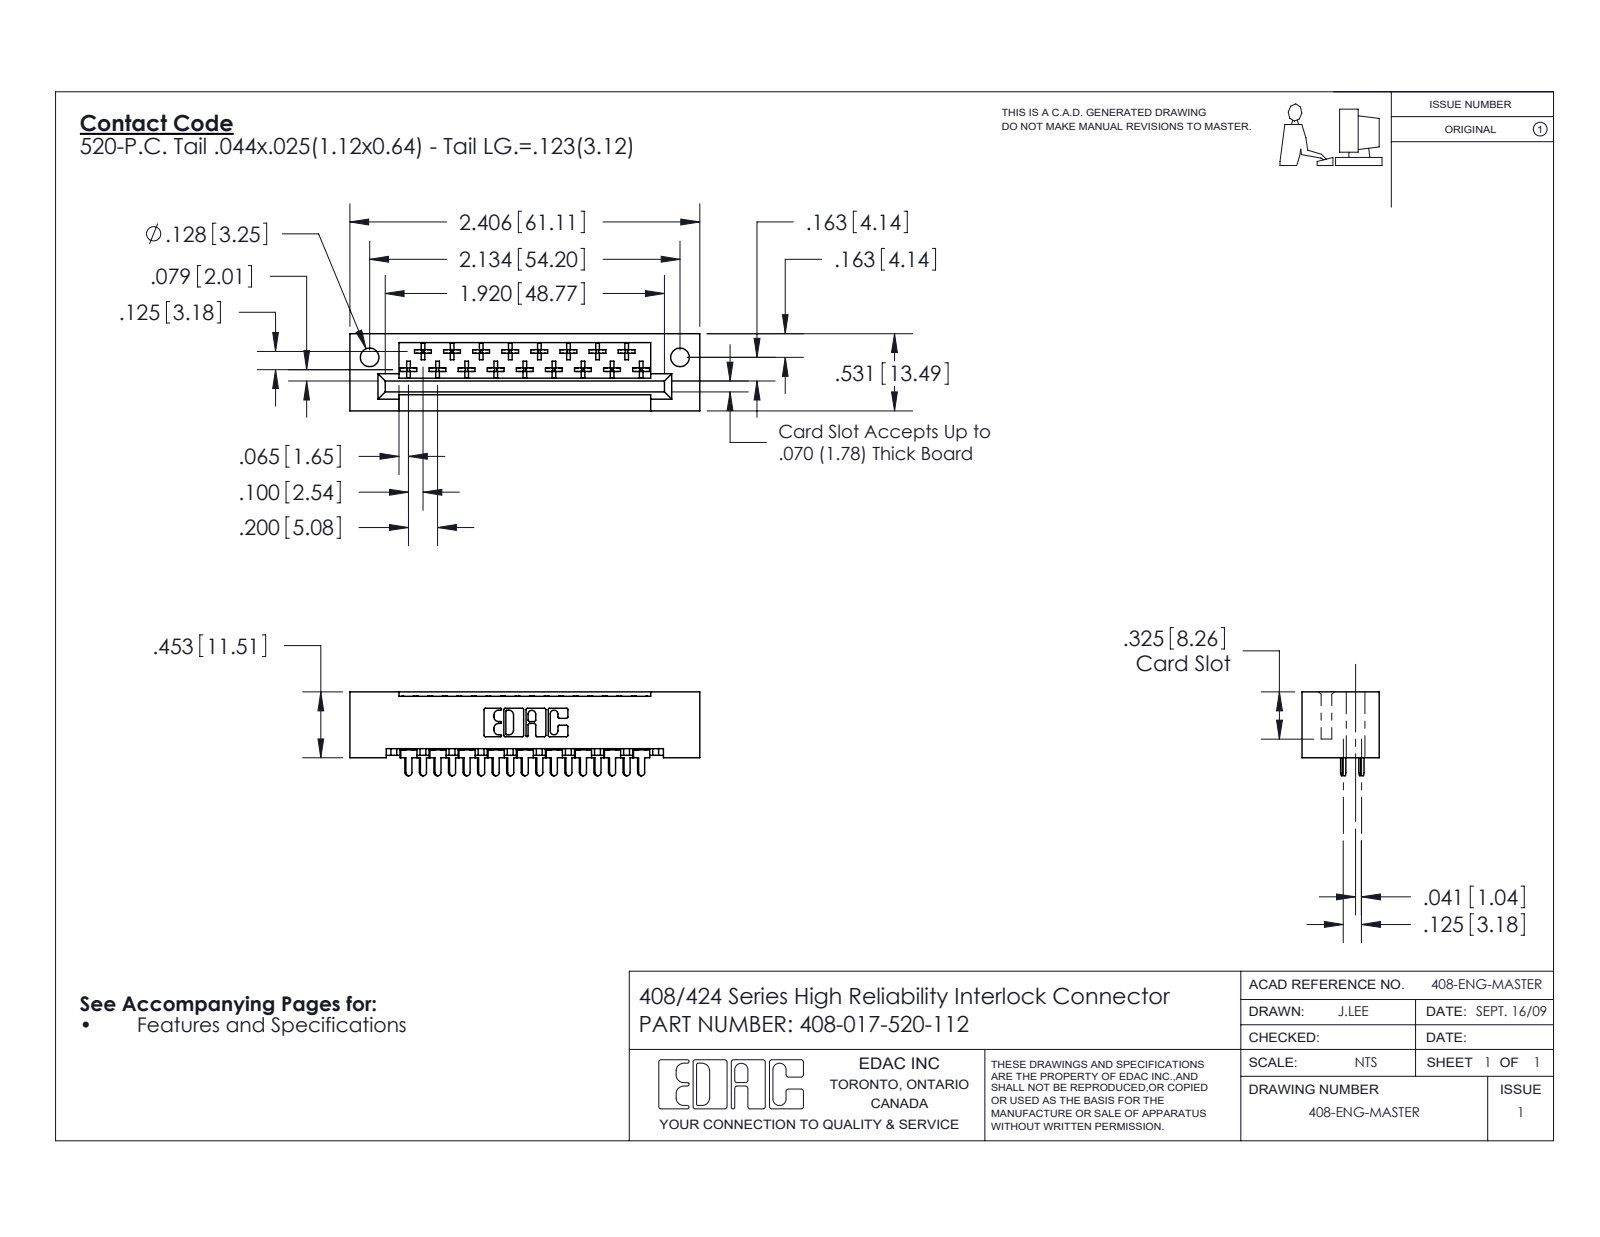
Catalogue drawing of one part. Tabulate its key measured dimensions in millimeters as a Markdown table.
| quantity | value |
| --- | --- |
| part name | 408-017-520-112; 408-290-001_408-290-120; 408 Part_017 - 1 |
| STEP written by | SolidWorks 2016 (CONFIG_CONTROL_DESIGN) |
| units | millimeters |
| bodies | 18 solids, 1062 faces (793 planar, 201 cylindrical, 68 other) |
| overall size | 61.1 × 14.6 × 13.5 |
| volume | 7 160 mm³ |
| surface area | 7 839 mm² |
| round holes (diameter × count) | 3.3 × 2 |
| partial cylindrical surfaces (radius × count) | 0.3 × 102, 0.3 × 22, 0.5 × 19, 0.6 × 17, 0.2 × 6, 0.8 × 6, 0.7 × 3 |
| main face-to-face distances | 10.2, 0.6, 13.5, 2.5, 0.6, 3.2, 6, 6.9, 7.5, 6.6 |
| hole center spacings | 54.2 |
